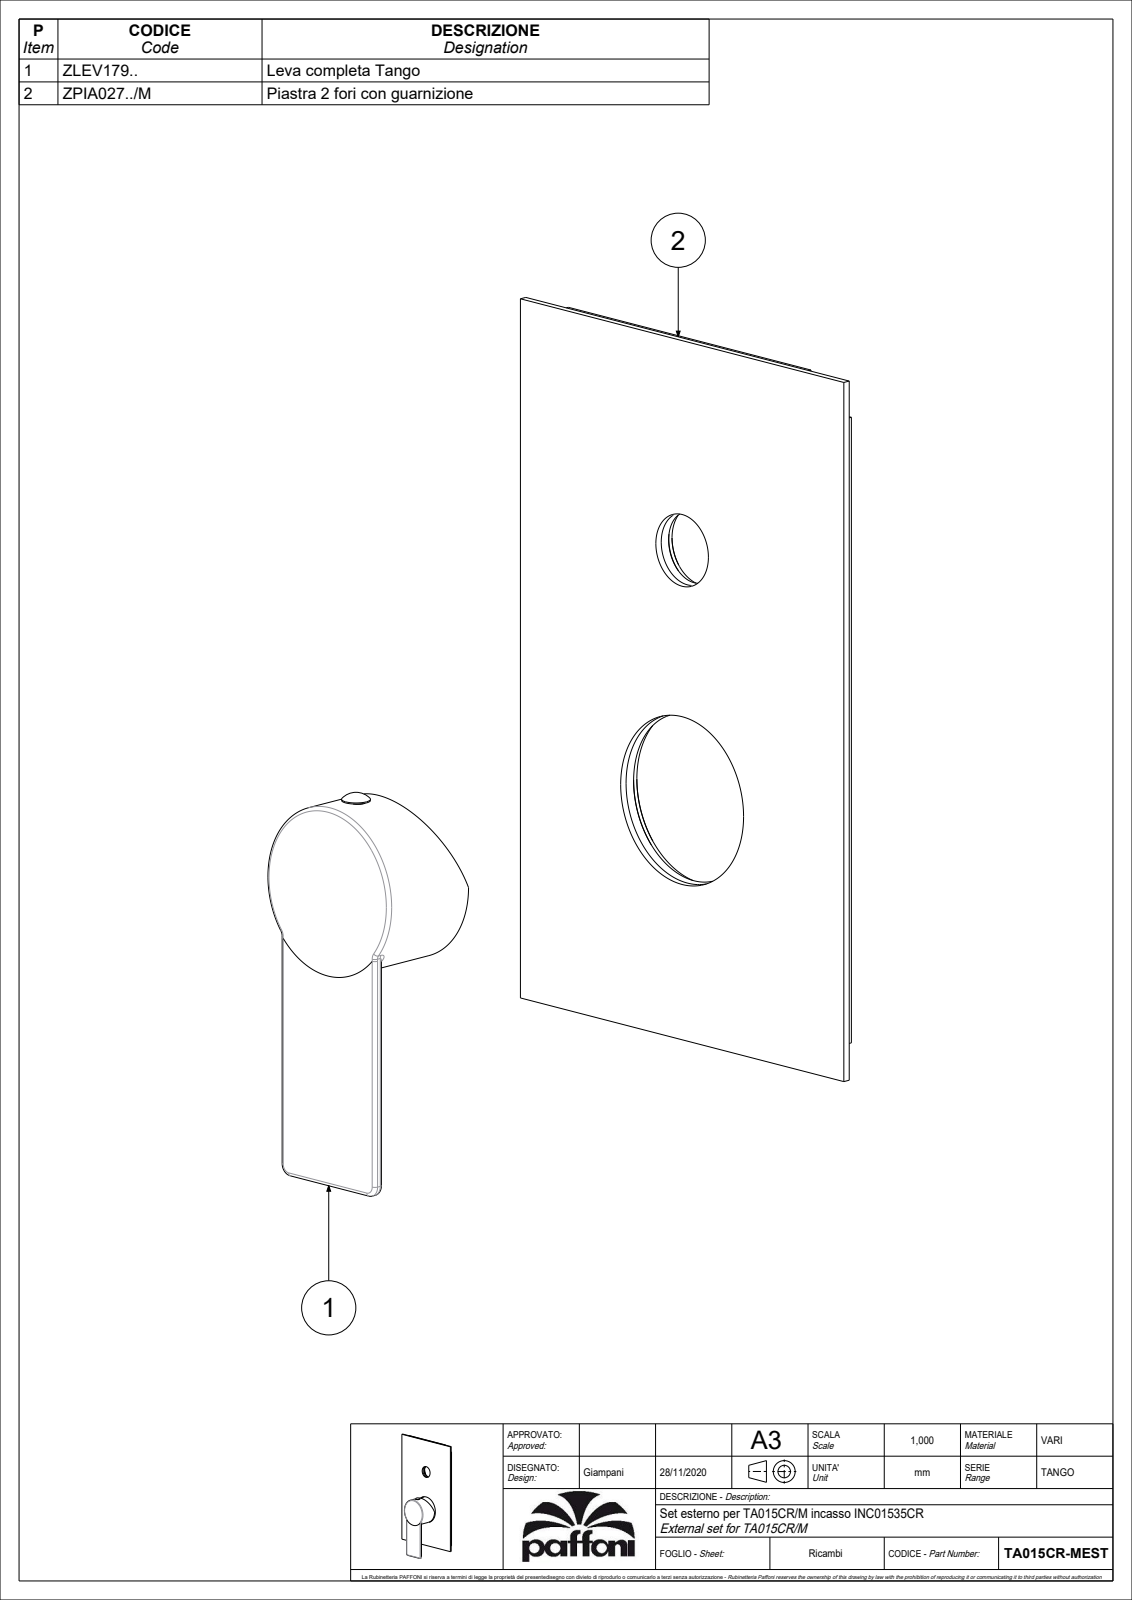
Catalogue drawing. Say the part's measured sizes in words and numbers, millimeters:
The part is named "TA015CR-MEST". Its 3-D file was written by "CREO PARAMETRIC BY PTC INC, 2020044 (CONFIG_CONTROL_DESIGN)". It is 2 solids with 171 faces: 73 planar, 51 cylindrical and 47 other. Overall it measures 205 by 120 by 39.5 millimeters. Its volume is 70 647 cubic millimeters and its surface area 64 600 square millimeters. Round holes: 1 of diameter 3, 1 of diameter 19.5, 1 of diameter 21.5, 1 of diameter 25, 1 of diameter 45.6, 1 of diameter 47.6, 1 of diameter 51.1. Round bosses or shafts: 1 of diameter 54.6, 1 of diameter 45.5, 1 of diameter 28.5, 1 of diameter 7.6, 1 of diameter 5.5, 1 of diameter 5. Partial cylindrical surfaces (rounded edges, fillets, slot ends): 6 of radius 1, 4 of radius 1.5, 2 of radius 0.5, 2 of radius 3, 1 of radius 3.5. The main face-to-face distances are 2, 0.8, 2.8, 34.3, 3, 28.5, 33.5, 31.5, 31.3, 30.5. The hole center spacings are 68.
